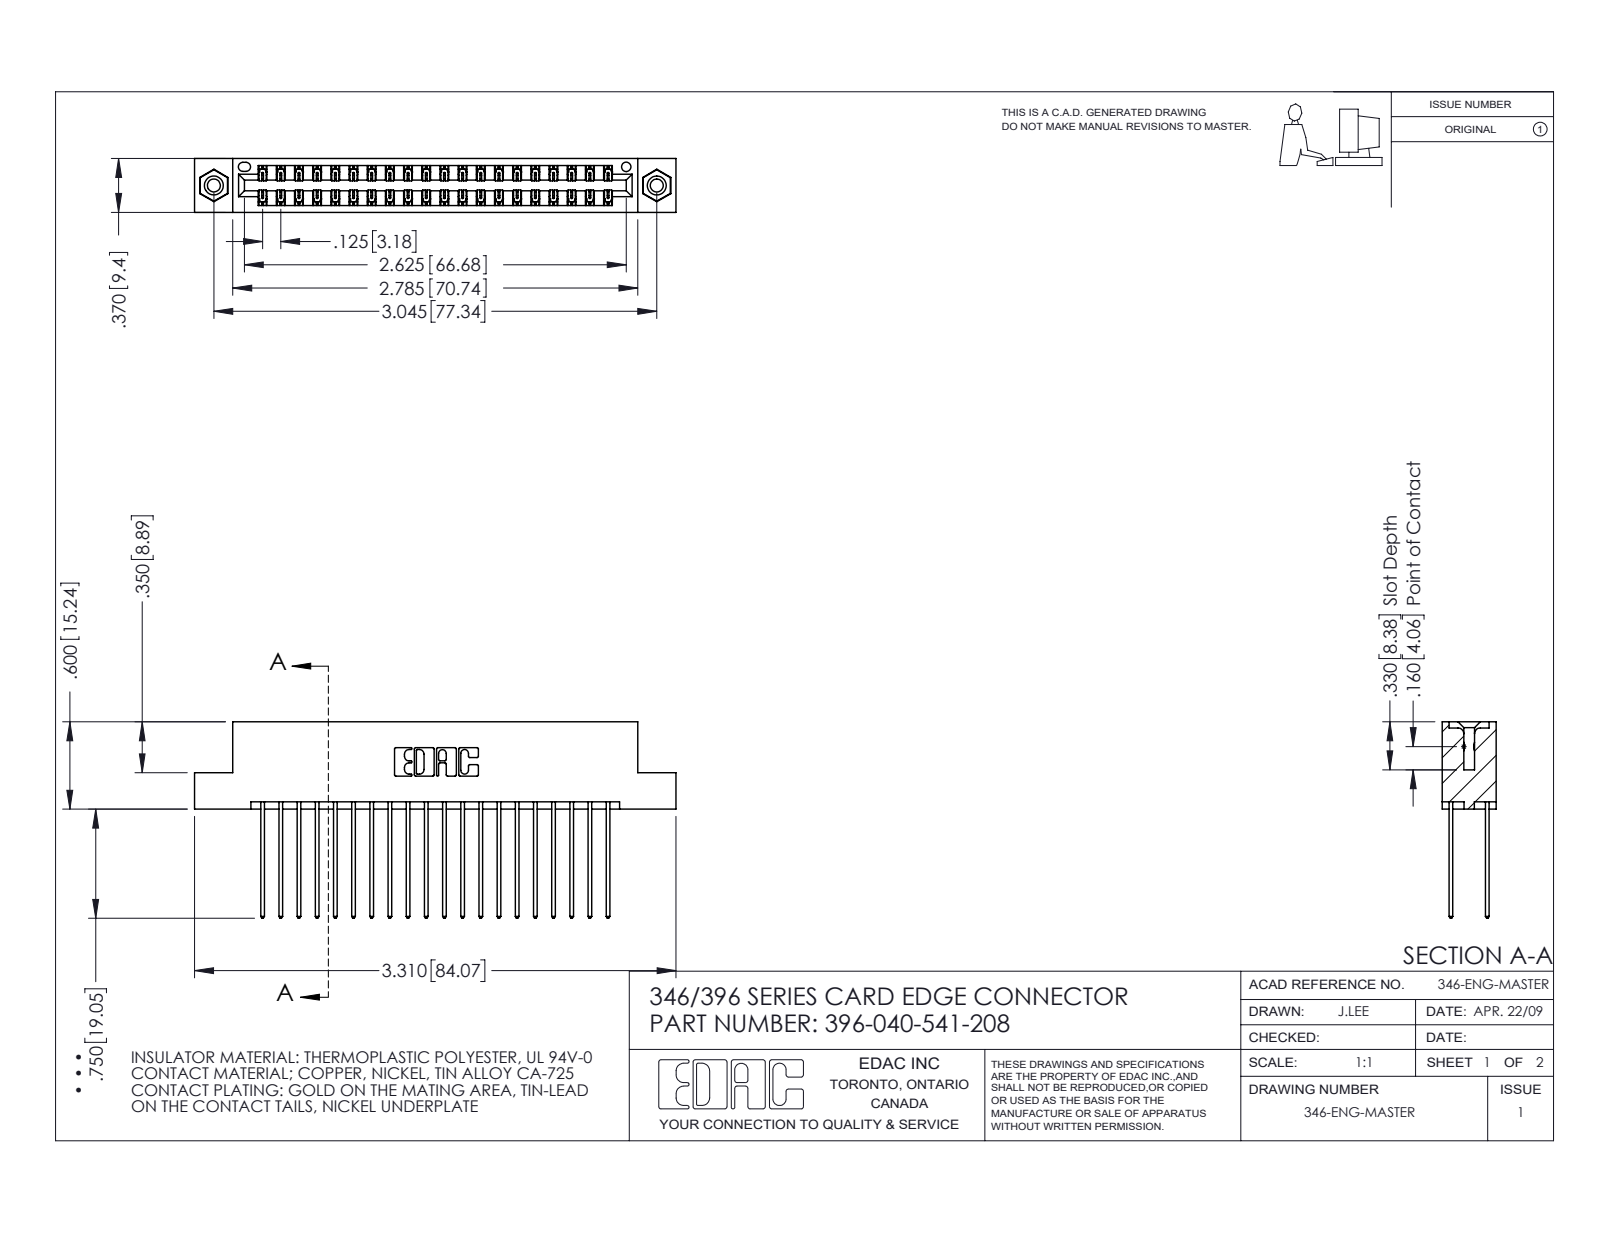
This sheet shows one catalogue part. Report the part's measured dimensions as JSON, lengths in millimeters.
{"part_name": "346 Part_Flush Mounting Lugs - 0.156 Dia-TI; 345-292-001_345-293-141; 345-250-001_345-250-003-102; 396-040-541-208", "step_written_by": "SolidWorks 2016 (CONFIG_CONTROL_DESIGN)", "units": "millimeters", "bodies": {"solids": 43, "faces": 2262, "planar": 1508, "cylindrical": 738, "other": 16}, "overall_size": [84.1, 34.3, 9.4], "volume_mm3": 8240, "surface_area_mm2": 12120, "round_holes": [[2.3, 2], [3.2, 2], [4, 2], [1.6, 1]], "round_bosses_or_shafts": [[3.9, 2]], "partial_cylinders_radius": [[0.2, 60], [0.3, 40], [0.3, 22], [0.2, 6], [0.8, 6], [0.7, 3], [0.4, 2], [0.6, 2]], "face_to_face_distances": [1.2, 8.2, 6.4, 1.8, 7.6, 0.6, 9.4, 7, 3.8, 5.6], "hole_center_spacings": [6.2, 72.1, 77.3]}
